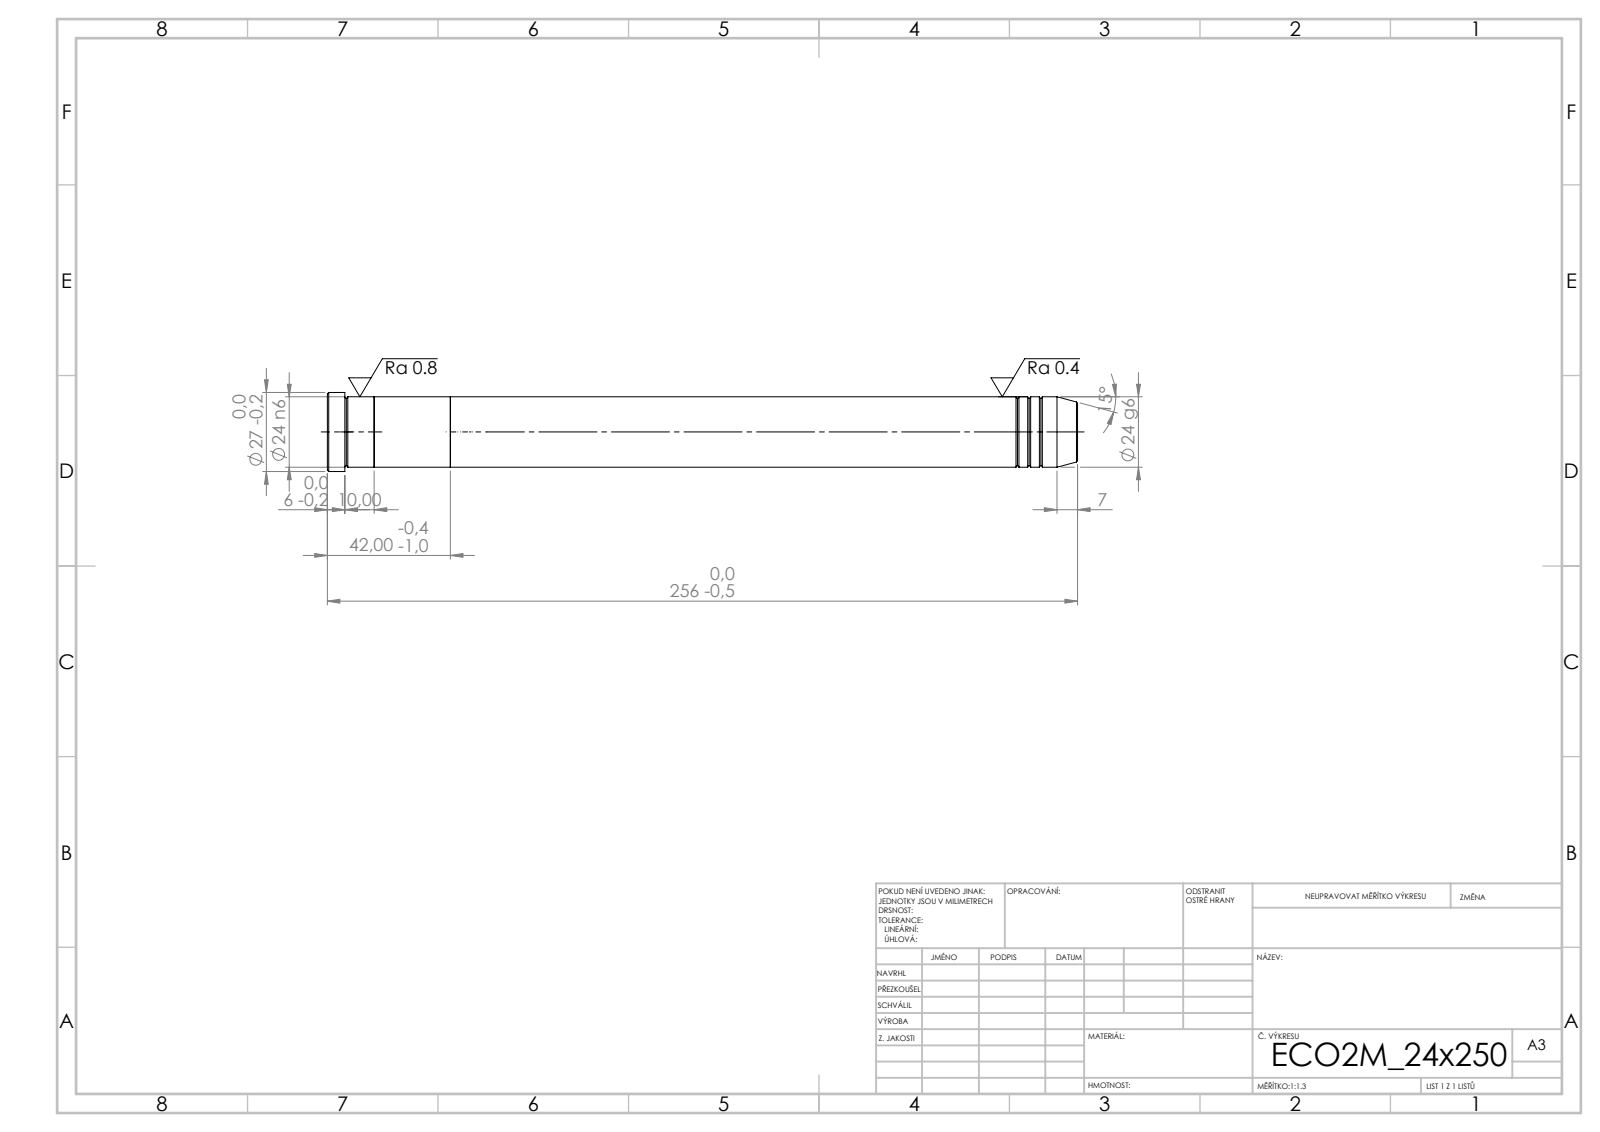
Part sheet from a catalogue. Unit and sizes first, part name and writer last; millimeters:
Units: millimetres
Overall size (bounding box): 256 × 27 × 27
Round bosses / shafts (diameter × count): ⌀27 ×1, ⌀24 ×1
Main face-to-face distances: 26, 42, 16, 214, 240, 256, 250, 36, 10, 6
Volume: 115 935 mm³ · Surface area: 22 286 mm²
Bodies: 3 solids, 43 faces (7 planar, 14 cylindrical, 22 other)
STEP written by: SolidWorks 2019 (CONFIG_CONTROL_DESIGN)
